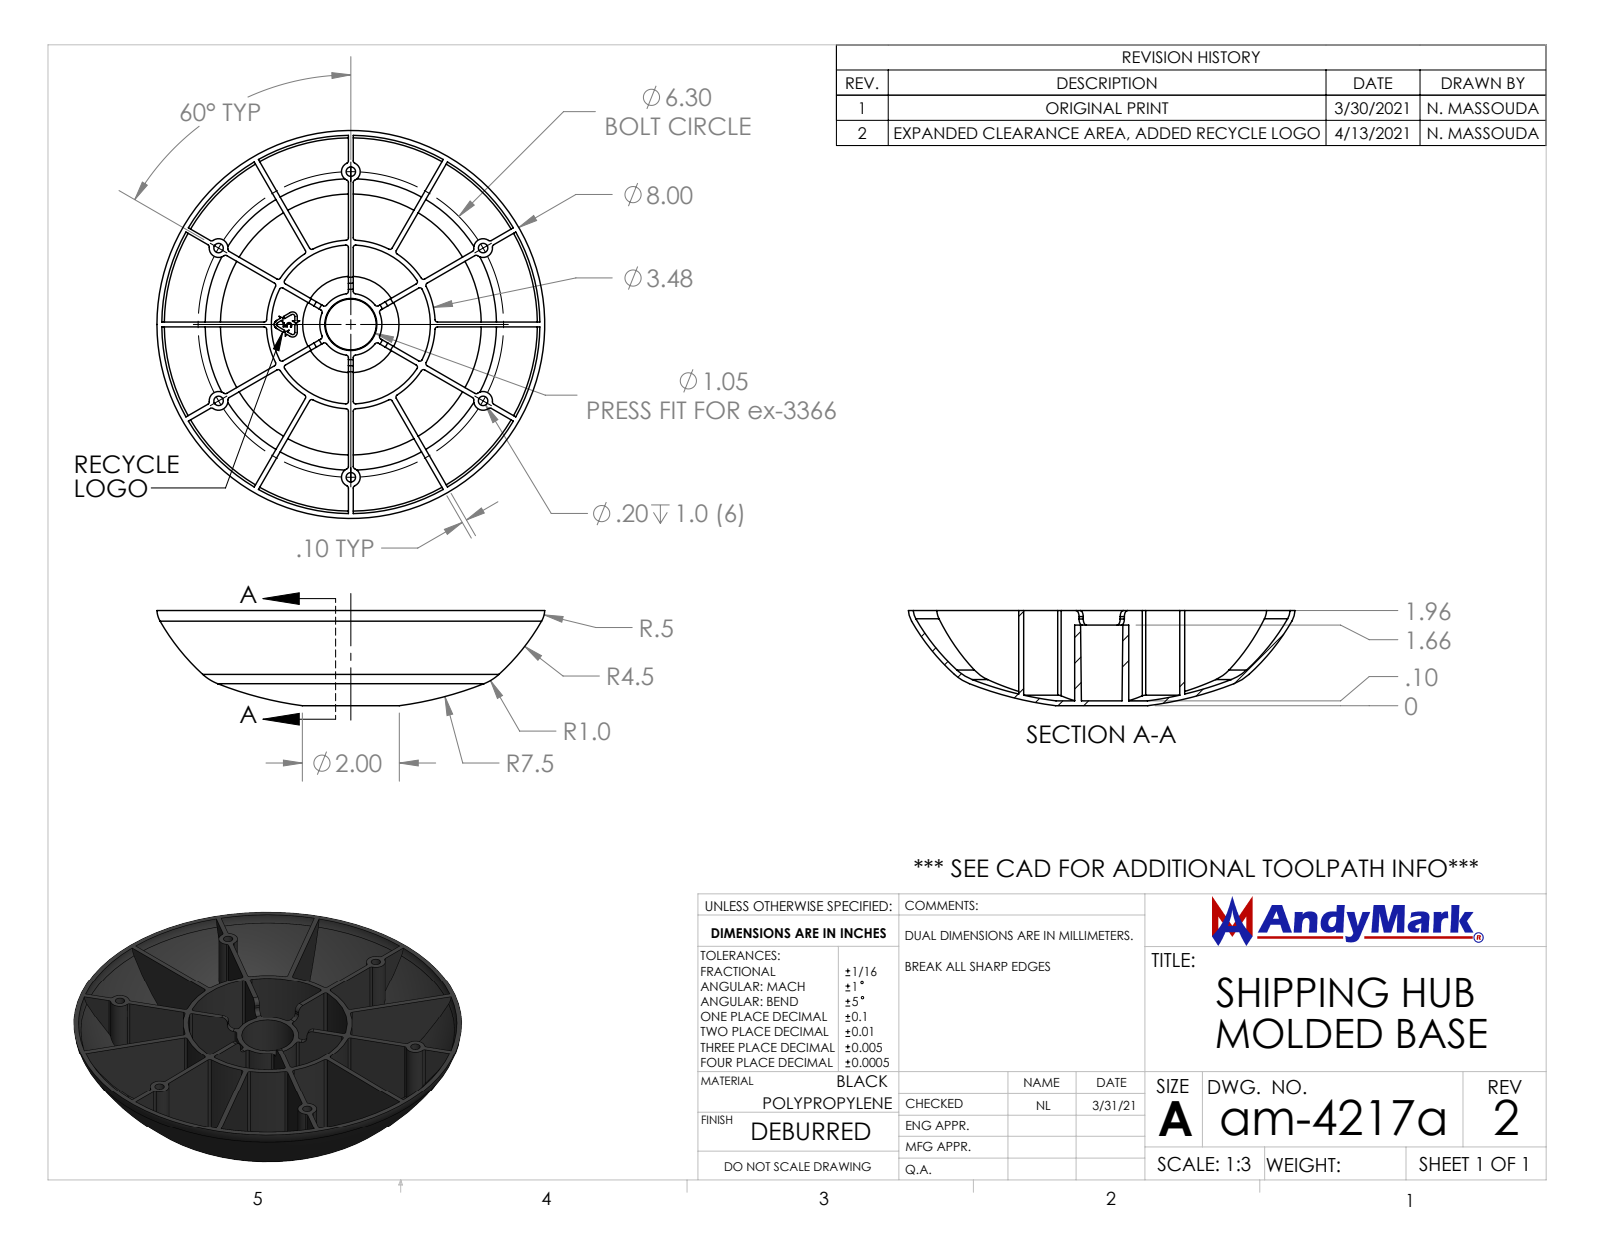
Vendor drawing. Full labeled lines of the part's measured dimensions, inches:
Part name (STEP PRODUCT): am-4217a Shipping Hub Molded Base
STEP written by: SolidWorks 2019 (CONFIG_CONTROL_DESIGN)
Units: inches
Bodies: 1 solid, 349 faces (97 planar, 145 cylindrical, 107 other)
Overall size (bounding box): 7.998 × 7.998 × 1.962
Volume: 13.61 in³ · Surface area: 264.2 in²
Round holes (diameter × count): ⌀0.196 ×6, ⌀3.28 ×1
Partial cylindrical surfaces — rounded edges, fillets, slot ends (radius × count): R0.05 ×72, R0.194 ×6, R0.64 ×1, R0.85 ×1, R1.74 ×1
Main face-to-face distances: 0.1, 1.963, 1.863, 1.663, 1.563, 0.3, 0.978, 0.878, 0.685, 0.985
Hole centre spacings: 3.15, 5.456, 5.456, 6.3, 6.3
